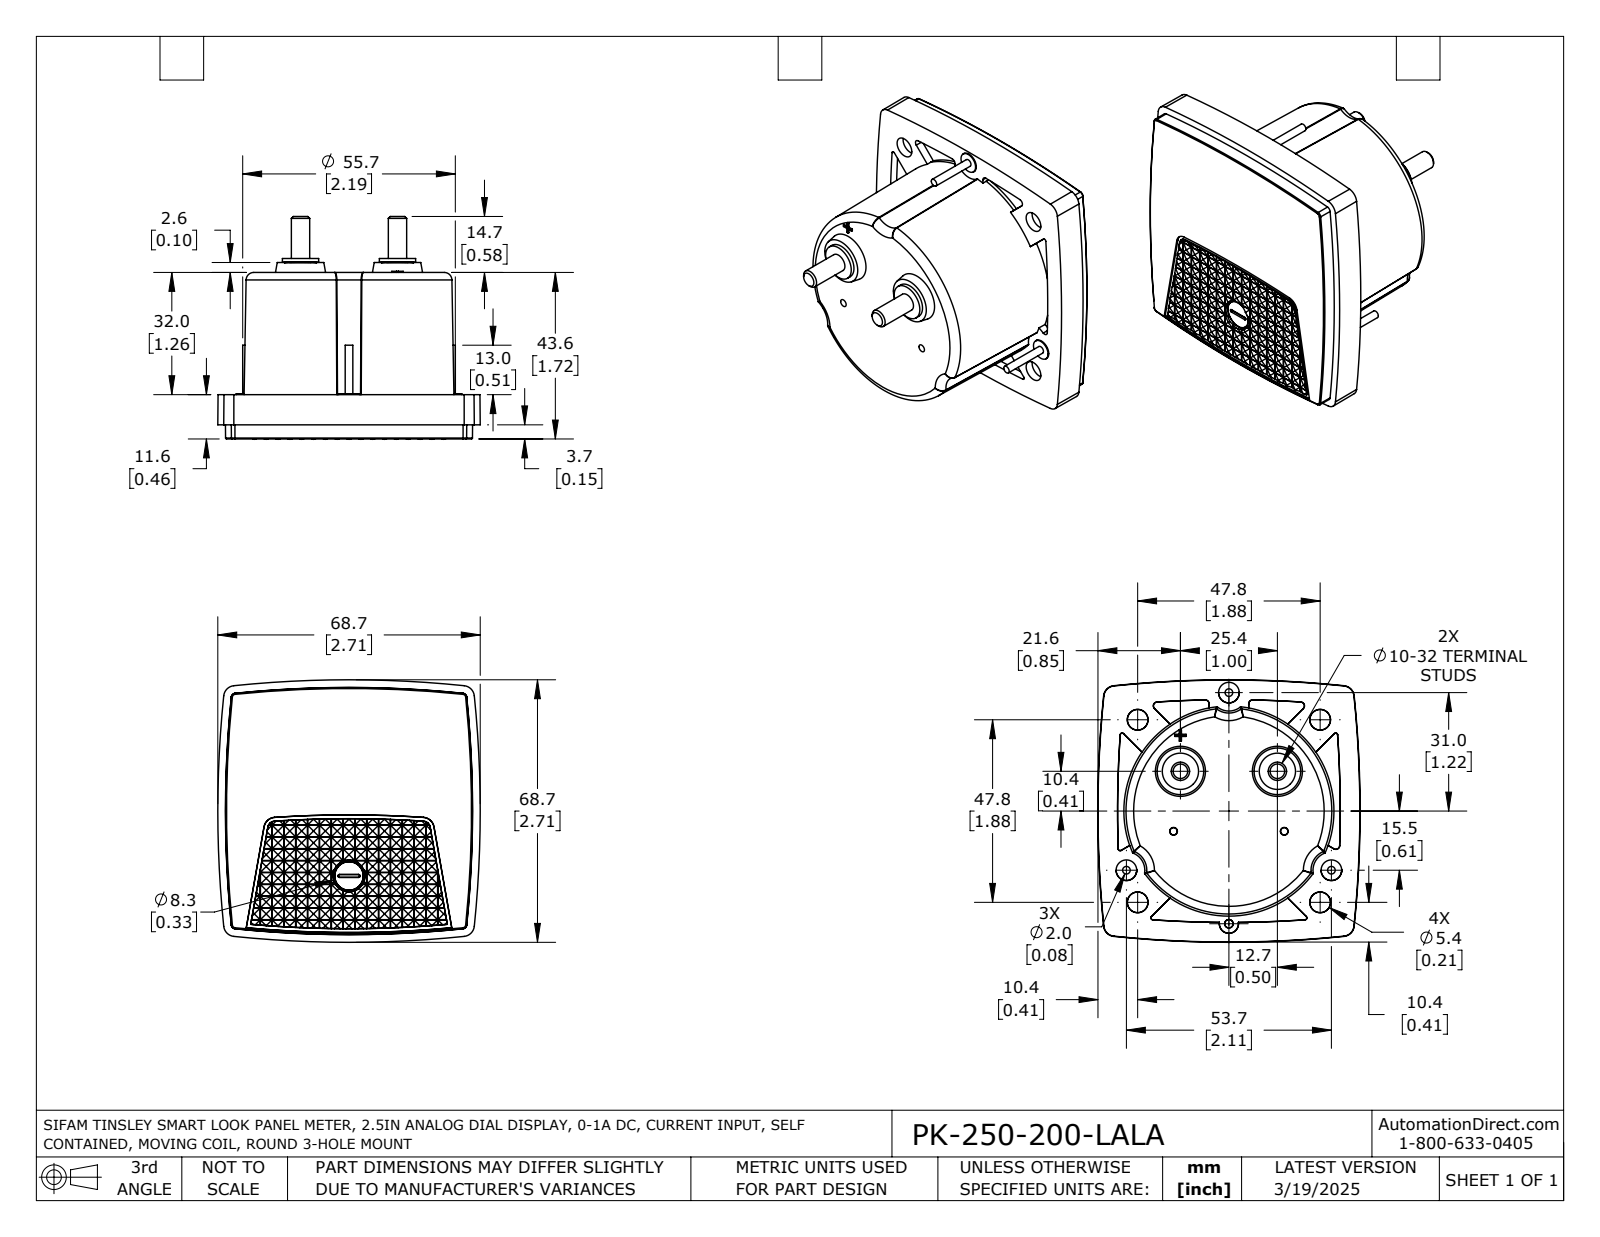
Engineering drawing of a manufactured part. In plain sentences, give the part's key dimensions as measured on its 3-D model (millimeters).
The part is named "PK-250-200-LALA". Its 3-D file was written by "SolidWorks 2021 (AUTOMOTIVE_DESIGN)". It is 1 solid with 1550 faces: 1165 planar, 265 cylindrical and 120 other. Overall it measures 68.7 by 68.7 by 58.3 millimeters. Its volume is 124 400 cubic millimeters and its surface area 19 620 square millimeters. Round bosses or shafts: 3 of diameter 5.4, 3 of diameter 2, 2 of diameter 9.5, 2 of diameter 4.8, 1 of diameter 5.5. Partial cylindrical surfaces (rounded edges, fillets, slot ends): 2 of radius 4.2, 1 of radius 27.5. The main face-to-face distances are 43.6, 32, 11.6, 0.6, 2.2, 2.4, 7.9, 3, 1.8, 34.2.
